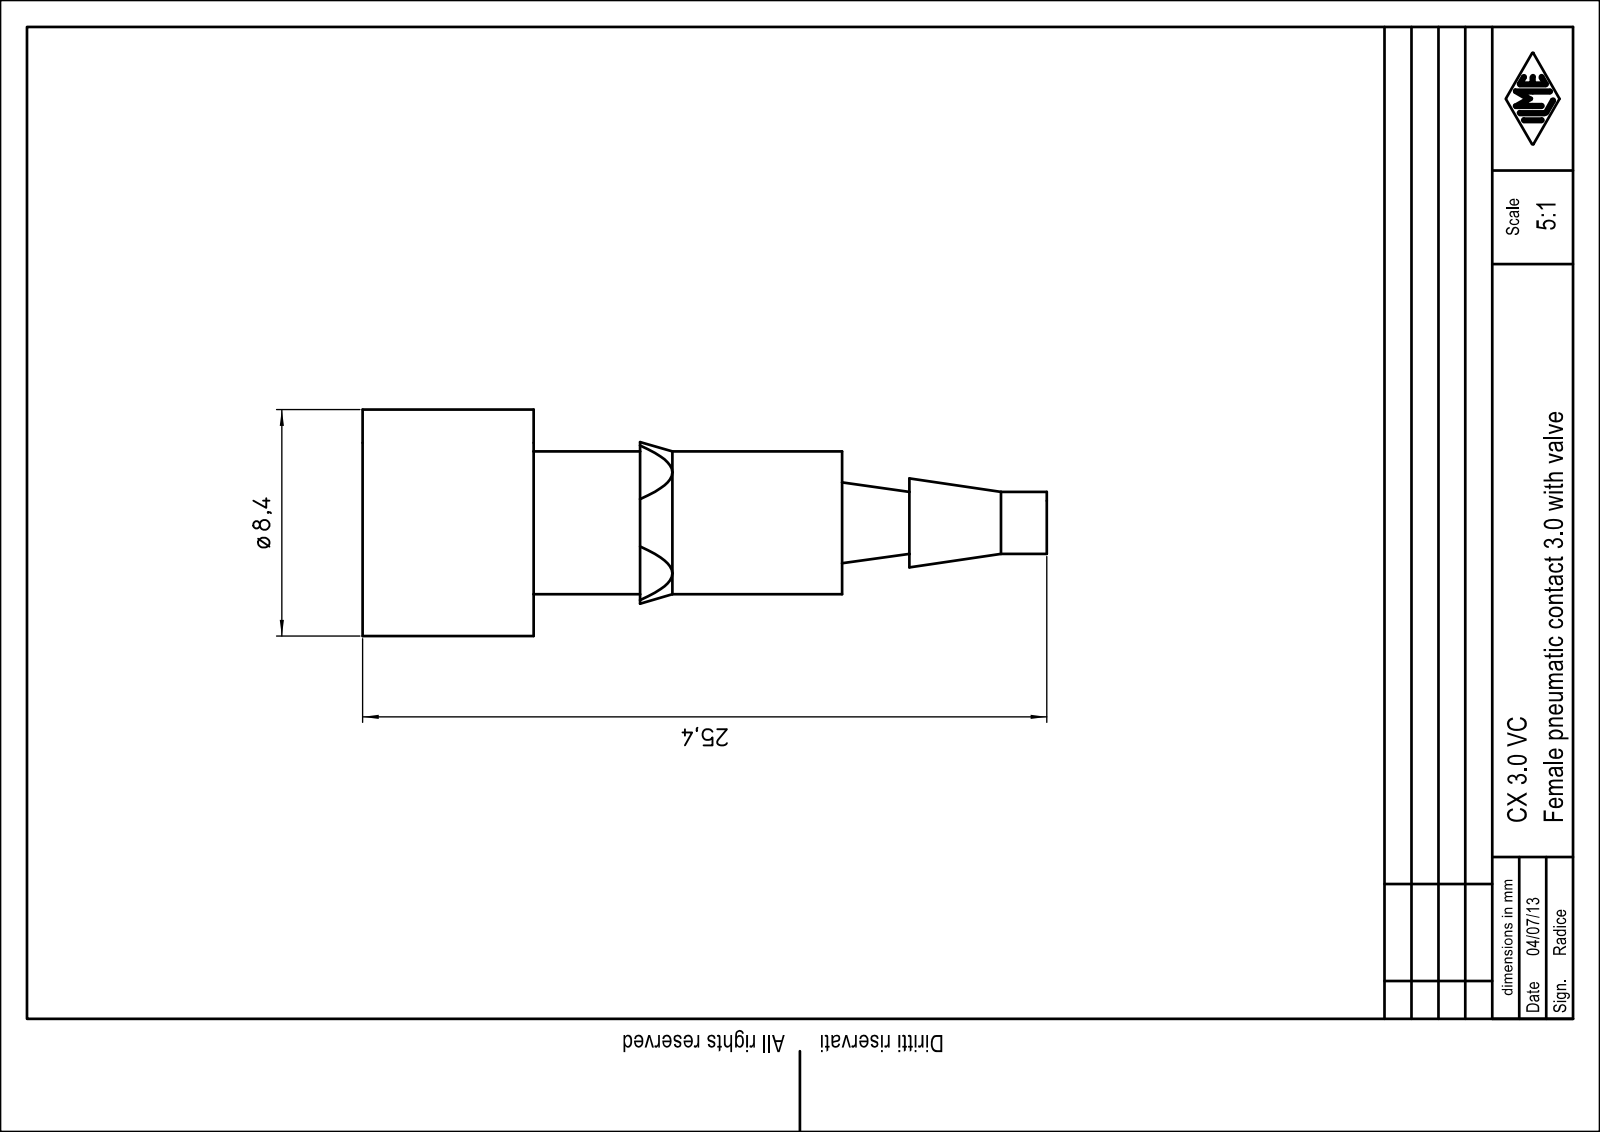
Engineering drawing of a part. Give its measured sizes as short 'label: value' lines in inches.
name: CX_3.0_VC
written by: PTC Creo Elements/Direct Modeling 19.0E 27-Jun-2016 (C) Parametric Technology GmbH (AUTOMOTIVE_DESIGN)
unit: in
bodies: 1 solid, 58 faces (32 planar, 18 cylindrical, 8 other)
size: 1 × 0.331 × 0.331
volume: 0.029 in³; area: 1.14 in²
holes: 1× ⌀0.061, 1× ⌀0.252
bosses: 1× ⌀0.331, 1× ⌀0.209, 1× ⌀0.114, 1× ⌀0.091
rounds: 1× R0.064
face distances: 0.209, 0.041, 0.25, 0.024, 0.451, 0.492, 0.701, 0.093, 0.116, 0.201
